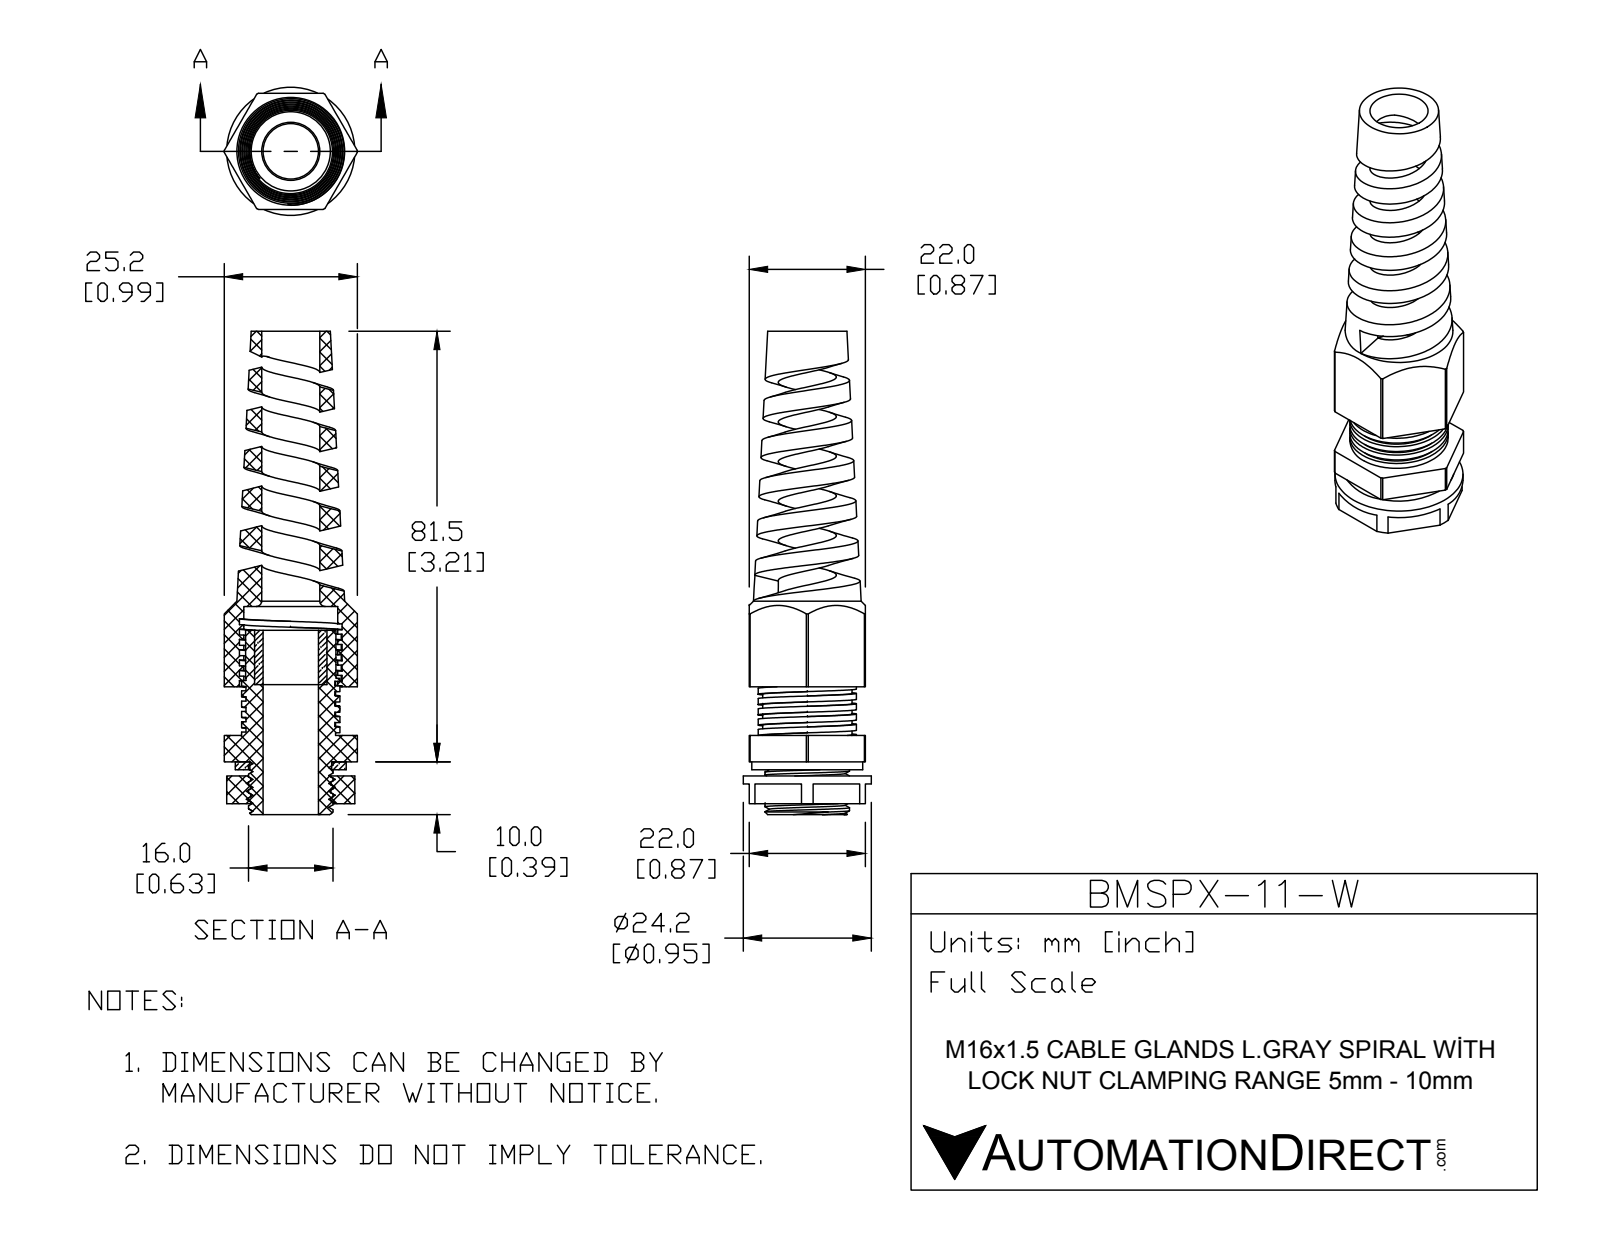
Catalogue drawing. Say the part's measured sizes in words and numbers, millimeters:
The part is named "BMSPX-11-W". Its 3-D file was written by "SolidWorks 2015 (CONFIG_CONTROL_DESIGN)". It is 5 solids with 231 faces: 103 planar, 93 cylindrical and 35 other. Overall it measures 91.5 by 25.2 by 24.24 millimeters. Its volume is 14 109 cubic millimeters and its surface area 15 386 square millimeters. Round holes: 1 of diameter 10.5, 1 of diameter 11, 1 of diameter 13.7, 1 of diameter 15.18, 1 of diameter 15.5, 1 of diameter 17.78. Round bosses or shafts: 1 of diameter 24.24, 1 of diameter 21, 1 of diameter 18.61, 1 of diameter 17.1, 1 of diameter 16. Partial cylindrical surfaces (rounded edges, fillets, slot ends): 1 of radius 12.6. The main face-to-face distances are 22, 2.68, 5.25, 7.93, 1.5, 12.93, 7.68, 5, 6.43, 1.18.
